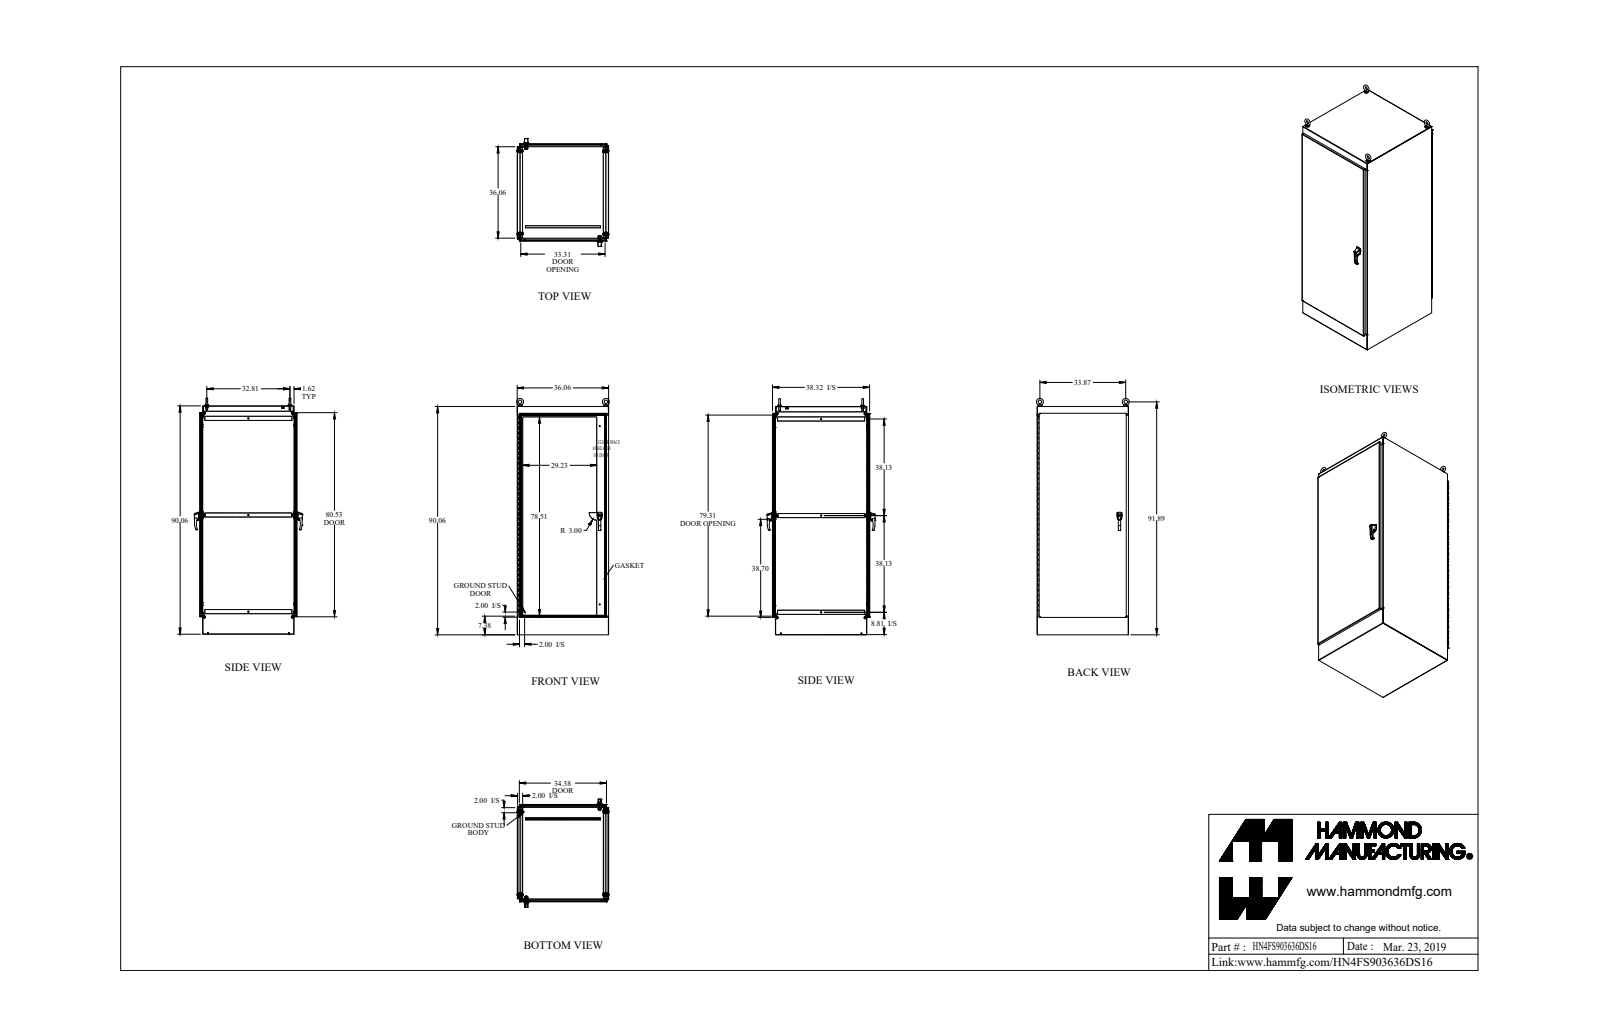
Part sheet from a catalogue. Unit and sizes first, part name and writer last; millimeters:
Units: millimetres
Overall size (bounding box): 2374.6 × 1083.7 × 929.7
Round holes (diameter × count): ⌀7.7 ×26, ⌀8.9 ×8, ⌀6.4 ×4, ⌀6.5 ×4, ⌀7.1 ×4, ⌀7.1 ×4, ⌀8 ×4, ⌀9.9 ×4, ⌀10.5 ×4, ⌀15.9 ×4, ⌀17.3 ×4, ⌀19.1 ×4
Round bosses / shafts (diameter × count): ⌀44.5 ×4, ⌀38.1 ×4, ⌀31.8 ×4, ⌀25.4 ×4, ⌀19.1 ×4, ⌀18.7 ×4, ⌀16 ×4, ⌀15.9 ×4
Partial cylindrical surfaces — rounded edges, fillets, slot ends (radius × count): R3.2 ×44, R1.1 ×42, R3.5 ×36, R0.5 ×32, R1.2 ×26, R3.6 ×26, R12.7 ×26, R1.5 ×21
Main face-to-face distances: 2.4, 913.5, 973.8, 911.1, 915.9, 971.4, 976.2, 2285.1, 30.1, 943.7
Hole centre spacings: 152.4, 304.8, 884.6, 457.2, 923.1, 984, 609.6, 1063.4
Volume: 30 180 000 mm³ · Surface area: 25 050 000 mm²
Bodies: 95 solids, 3657 faces (1586 planar, 1743 cylindrical, 328 other)
Part name (STEP PRODUCT): HN4FS903636DS16
STEP written by: SolidWorks 2018 (AUTOMOTIVE_DESIGN)
